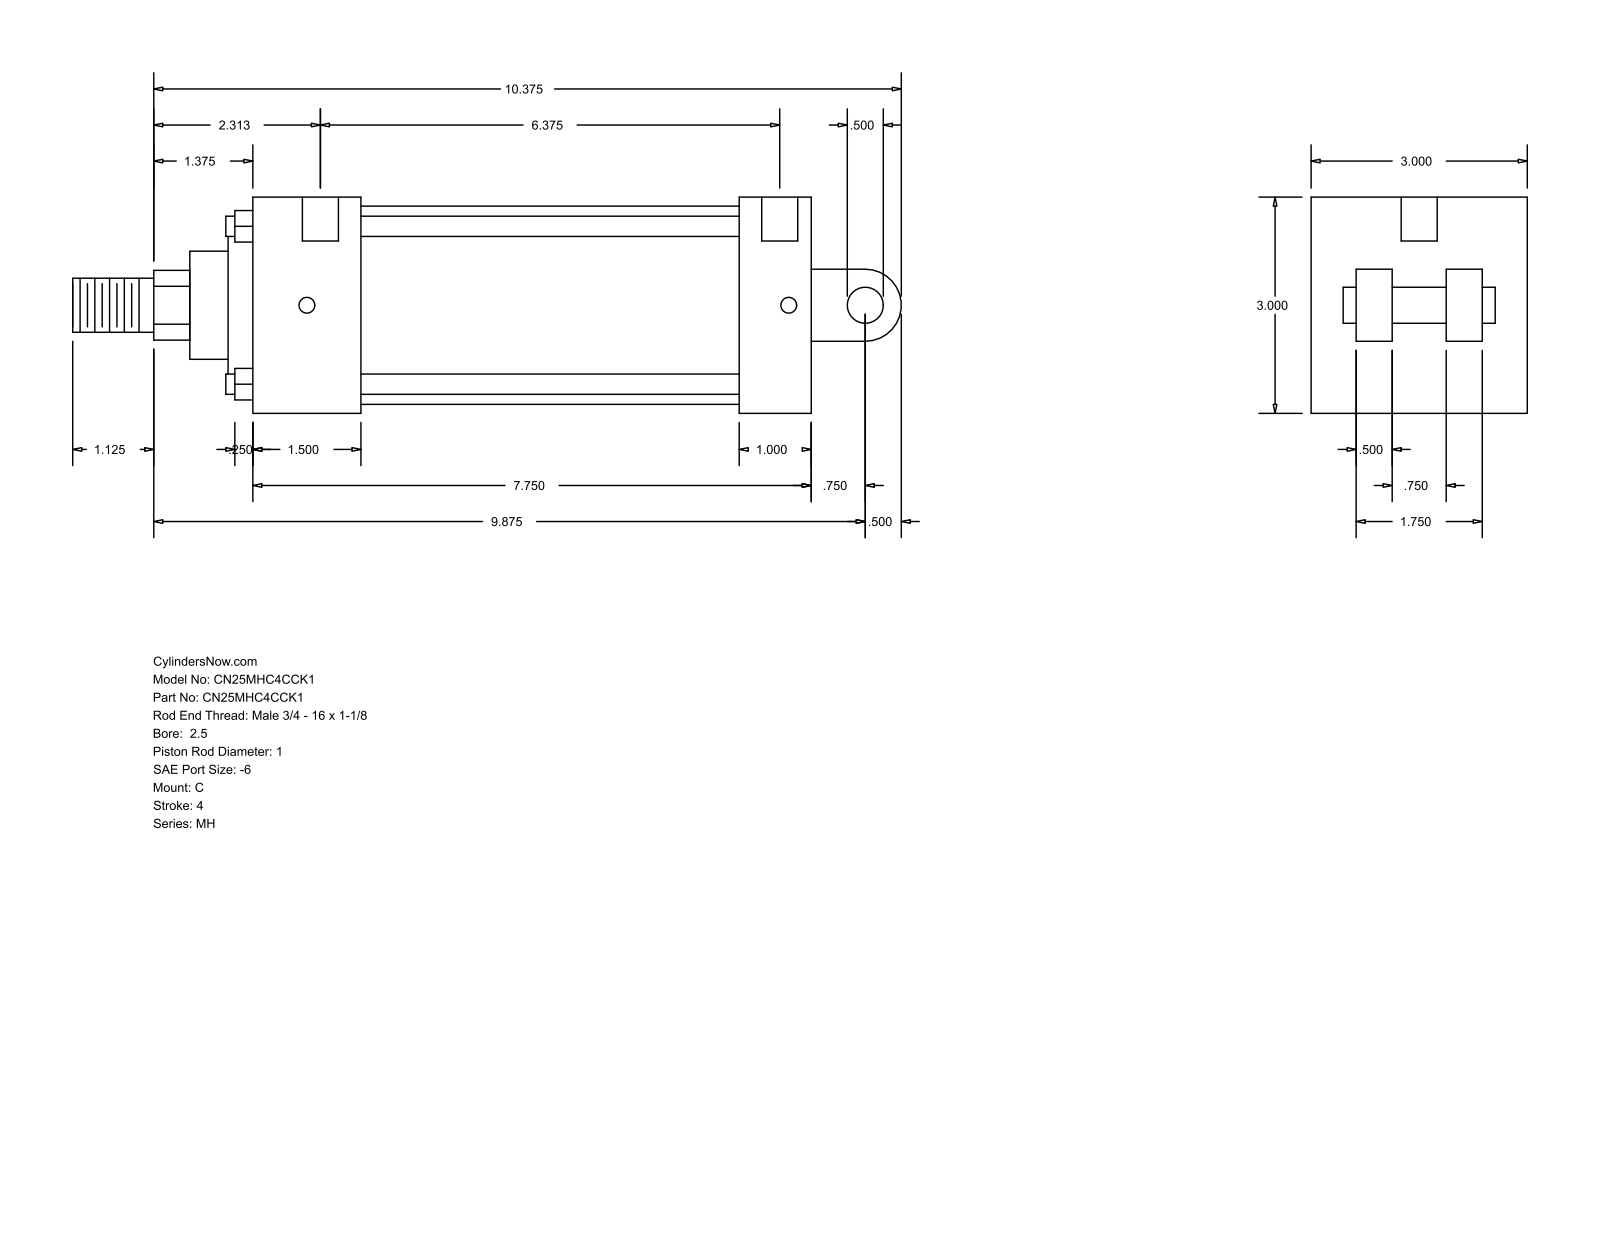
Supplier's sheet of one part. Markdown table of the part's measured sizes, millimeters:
| quantity | value |
| --- | --- |
| part name | MH_C__0250_1 |
| STEP written by | GSSL Pune (CONFIG_CONTROL_DESIGN) |
| units | millimeters |
| bodies | 0 solids, 101 faces (71 planar, 30 cylindrical, 0 other) |
| overall size | 292.1 × 76.2 × 76.2 |
| round holes (diameter × count) | 5.56 × 4, 12.7 × 2 |
| round bosses / shafts (diameter × count) | 7.14 × 4, 69.85 × 1, 60.33 × 1, 38.1 × 1, 25.4 × 1, 19.05 × 1, 12.7 × 1 |
| partial cylindrical surfaces (radius × count) | 12.29 × 1, 12.7 × 1 |
| main face-to-face distances | 76.2, 25.4, 196.86, 60.33, 15.87, 171.46, 38.11, 133.35, 158.75, 12.7 |
| hole center spacings | 169.86, 3.18, 4.76, 161.92, 165.1, 166.68 |
